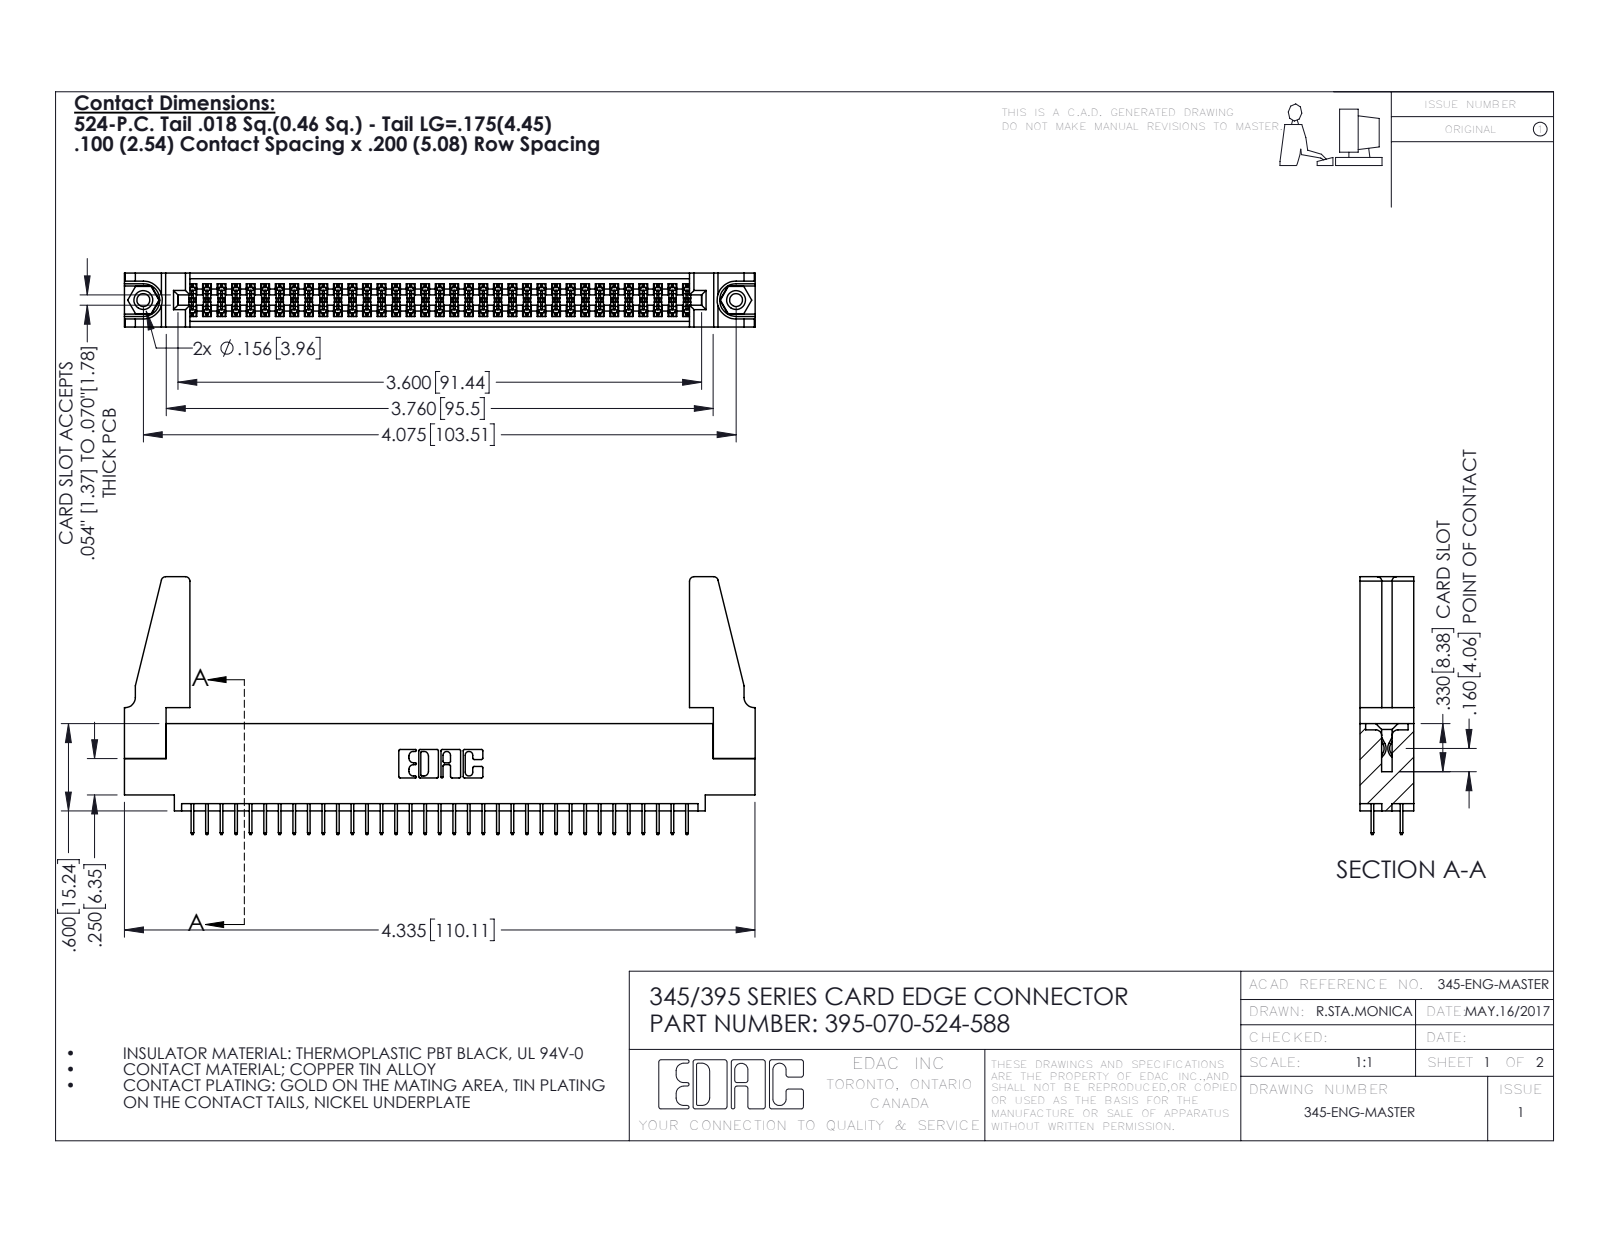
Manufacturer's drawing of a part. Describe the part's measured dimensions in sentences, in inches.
The part is named "395-070-524-588; 345 Part_0.110 Offset - 0.156 Dia-TH; 345-250-001_345-250-001-102; 345-220-078_345-220-088 (+1 more)". Its 3-D file was written by "SolidWorks 2016 (CONFIG_CONTROL_DESIGN)". It is 75 solids with 4034 faces: 2886 planar, 1132 cylindrical and 16 other. Overall it measures 4.336 by 1.772 by 0.37 inches. Its volume is 0.836 cubic inches and its surface area 28.29 square inches. Round holes: 2 of diameter 0.089, 2 of diameter 0.125, 2 of diameter 0.156, 1 of diameter 0.064. Round bosses or shafts: 2 of diameter 0.155. Partial cylindrical surfaces (rounded edges, fillets, slot ends): 105 of radius 0.006, 22 of radius 0.01, 8 of radius 0.03, 6 of radius 0.007, 6 of radius 0.031, 3 of radius 0.026, 2 of radius 0.014, 2 of radius 0.019. The main face-to-face distances are 0.072, 0.298, 0.37, 0.2, 0.098, 0.272, 0.025, 0.225, 0.072, 0.175. The hole center spacings are 0.27, 3.839, 4.075.
